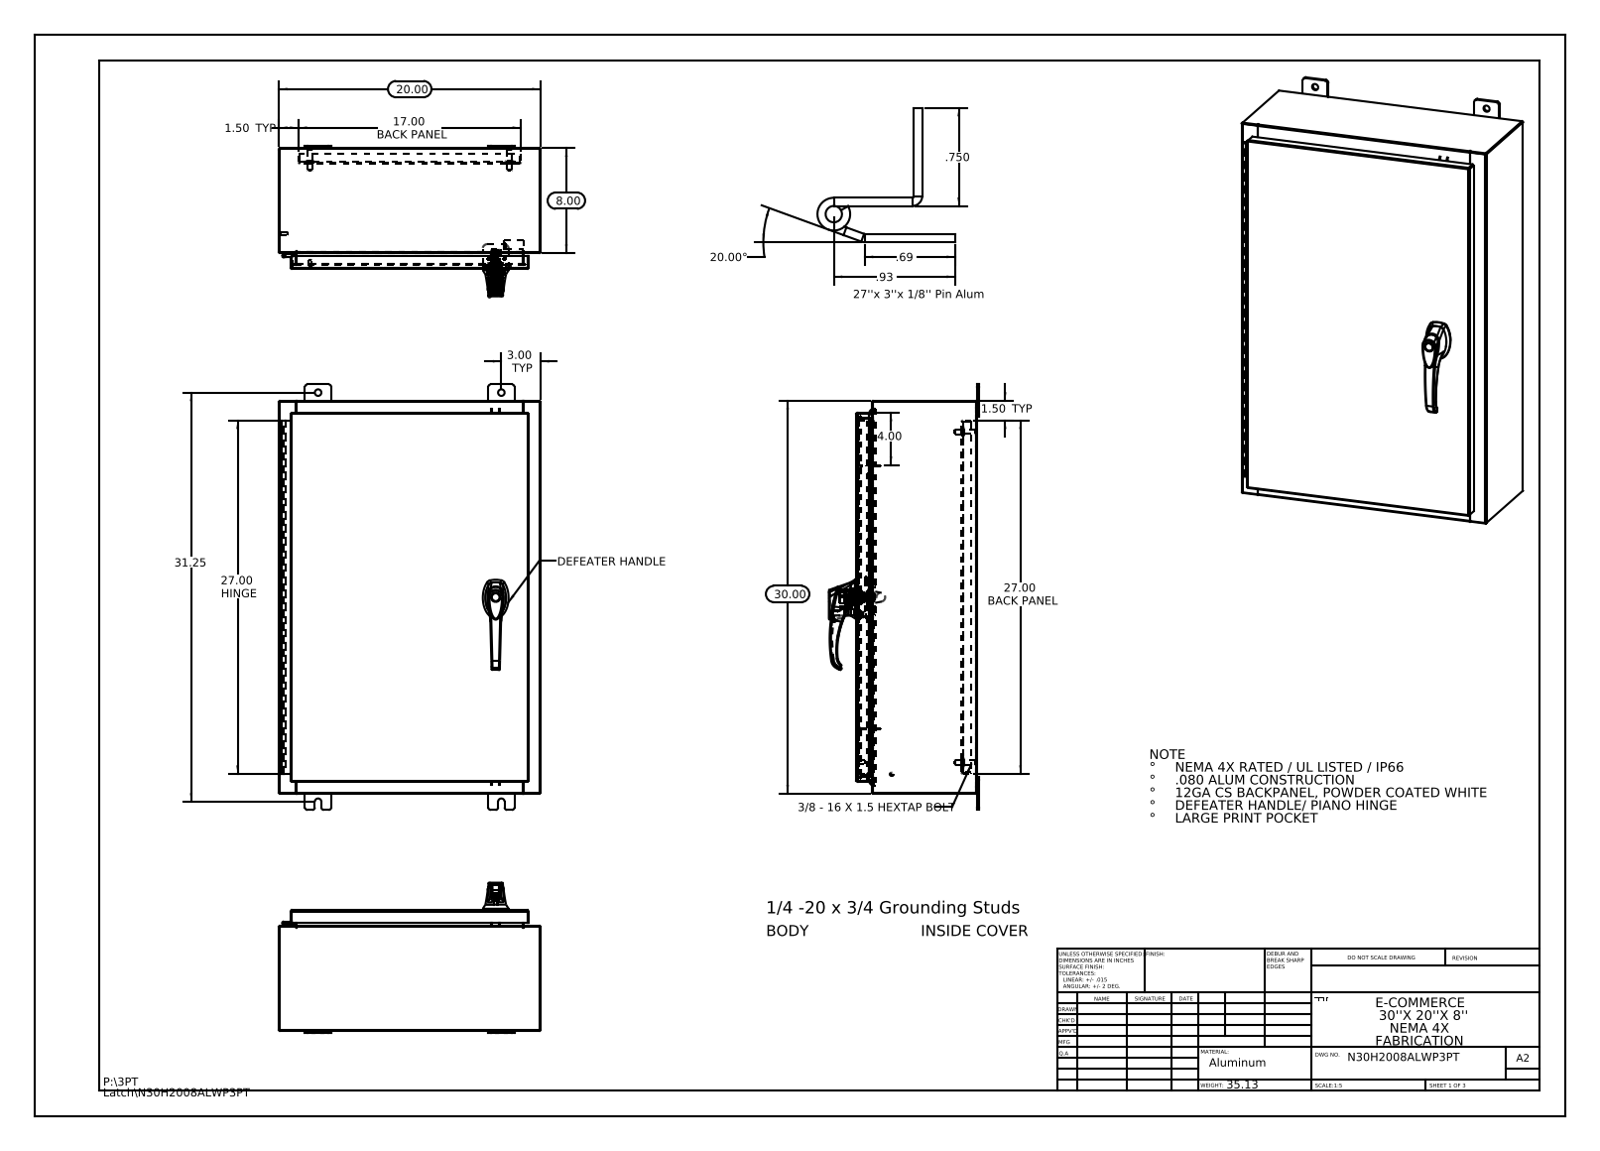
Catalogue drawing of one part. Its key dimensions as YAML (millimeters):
part_name: "NMP-SS-RODGUIDES; N30H2008ALWP3PT Top; N30H2008ALWP3PT Backpanel; N30H2008ALWP3PT 125 Pin Hinge (+8 more)"
step_written_by: "SolidWorks 2013 (CONFIG_CONTROL_DESIGN)"
units: millimeters
bodies: {solids: 37, faces: 2662, planar: 971, cylindrical: 993, other: 698}
overall_size: [825.5, 508, 292]
volume: 3874000
surface_area: 3770000
round_holes:
  - {diameter: 12.7, count: 8}
  - {diameter: 6.4, count: 4}
  - {diameter: 3.5, count: 3}
  - {diameter: 4.1, count: 3}
  - {diameter: 2, count: 2}
  - {diameter: 5.2, count: 2}
  - {diameter: 8, count: 2}
  - {diameter: 11.1, count: 2}
  - {diameter: 3.2, count: 1}
  - {diameter: 3.2, count: 1}
  - {diameter: 5, count: 1}
  - {diameter: 7, count: 1}
round_bosses_or_shafts:
  - {diameter: 15.9, count: 4}
  - {diameter: 9.5, count: 4}
  - {diameter: 8.4, count: 4}
  - {diameter: 4, count: 4}
  - {diameter: 3.6, count: 4}
  - {diameter: 8, count: 3}
  - {diameter: 6, count: 3}
  - {diameter: 30, count: 1}
partial_cylinders:
  - {radius: 3, count: 37}
  - {radius: 0.2, count: 33}
  - {radius: 0.3, count: 24}
  - {radius: 4.8, count: 24}
  - {radius: 2.2, count: 18}
  - {radius: 1, count: 15}
  - {radius: 0.7, count: 12}
  - {radius: 0.2, count: 6}
face_to_face_distances: [1.9, 231.8, 2.6, 229.9, 233.7, 506.1, 25.4, 27.3, 204.5, 206.4]
hole_center_spacings: [212.6, 384.6, 7.5, 15.9, 21.4, 31.8, 33.4, 39.6]
